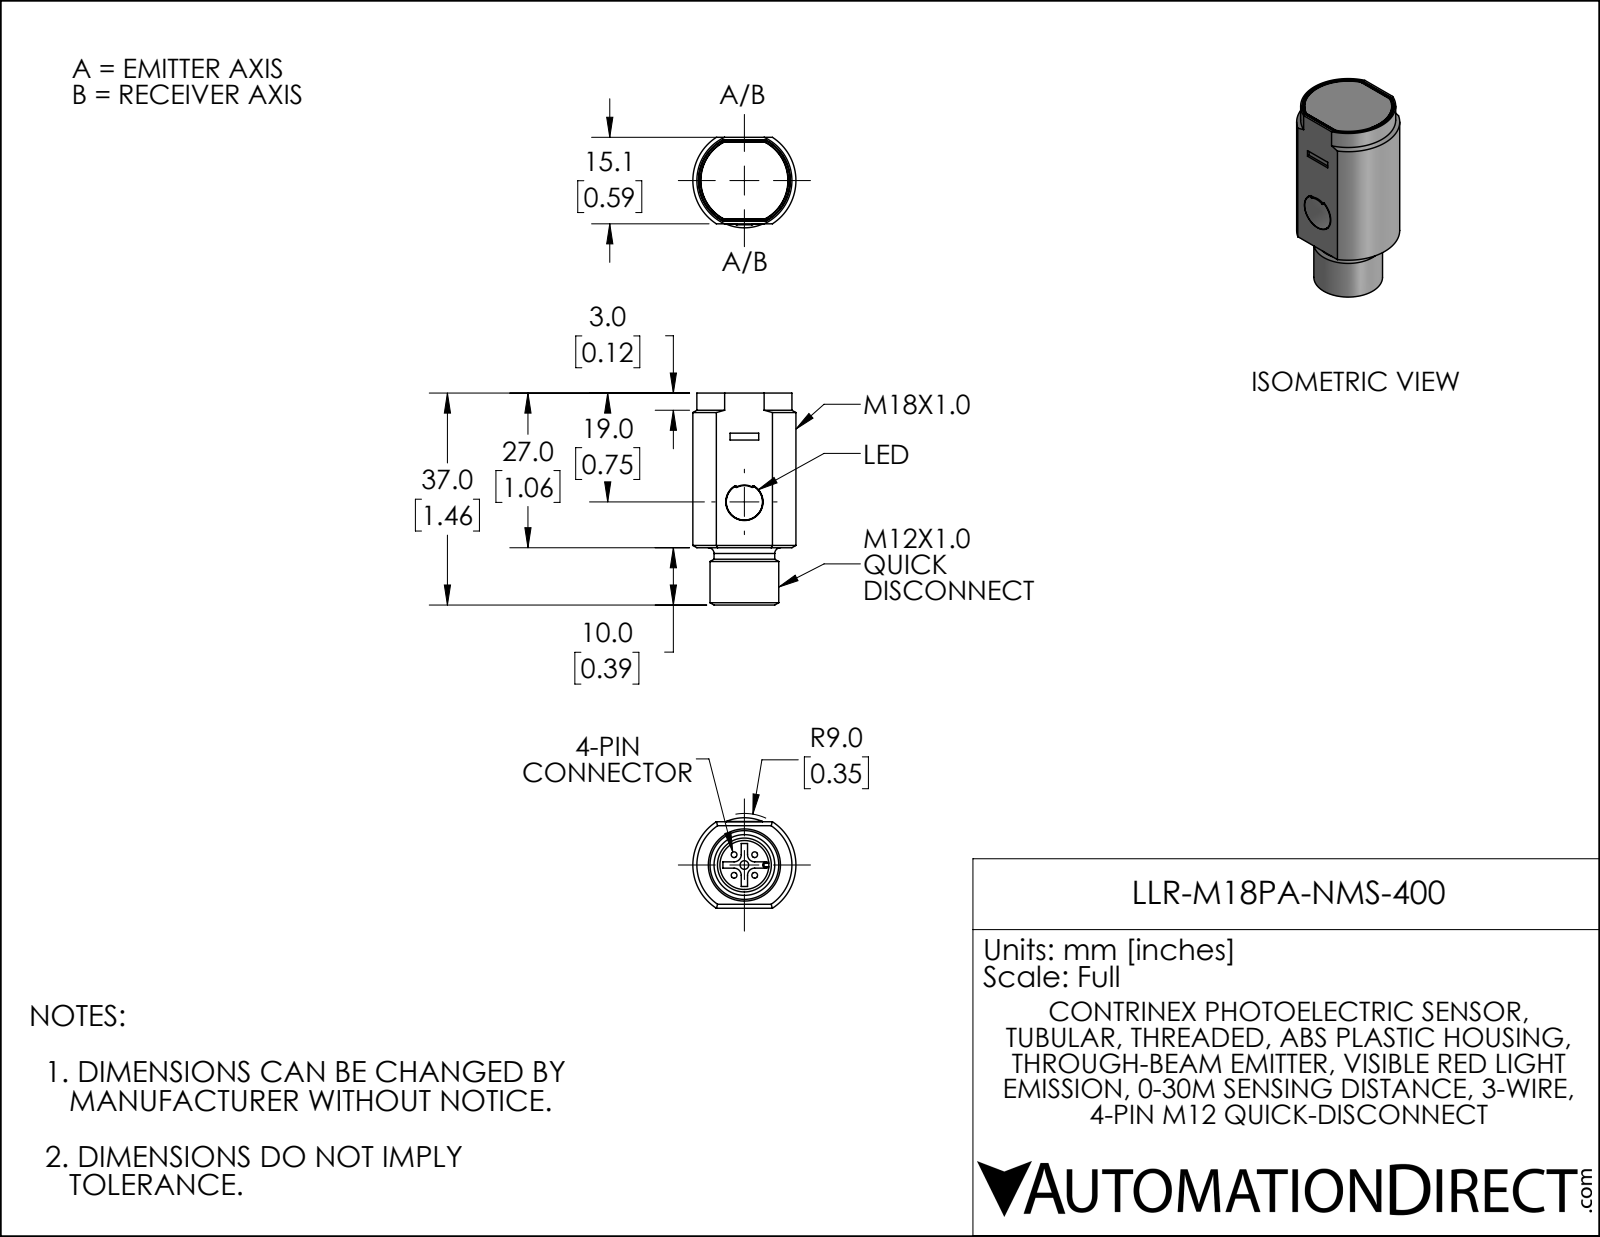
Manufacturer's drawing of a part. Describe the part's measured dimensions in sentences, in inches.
The part is named "LLR-M18PA-NMS-400". Its 3-D file was written by "SolidWorks 2021 (AUTOMOTIVE_DESIGN)". It is 1 solid with 125 faces: 56 planar, 54 cylindrical and 15 other. Overall it measures 1.457 by 0.709 by 0.622 inches. Its volume is 0.418 cubic inches and its surface area 4.241 square inches. Round holes: 1 of diameter 0.059, 1 of diameter 0.256, 1 of diameter 0.336. Round bosses or shafts: 4 of diameter 0.039, 1 of diameter 0.472, 1 of diameter 0.417. Partial cylindrical surfaces (rounded edges, fillets, slot ends): 8 of radius 0.006, 8 of radius 0.014, 8 of radius 0.028, 4 of radius 0.049, 2 of radius 0.008, 1 of radius 0.02, 1 of radius 0.112, 1 of radius 0.116. The main face-to-face distances are 0.594, 1.061, 0.047, 1.108, 1.063, 1.11, 0.016, 1.457, 1.455, 0.394.
